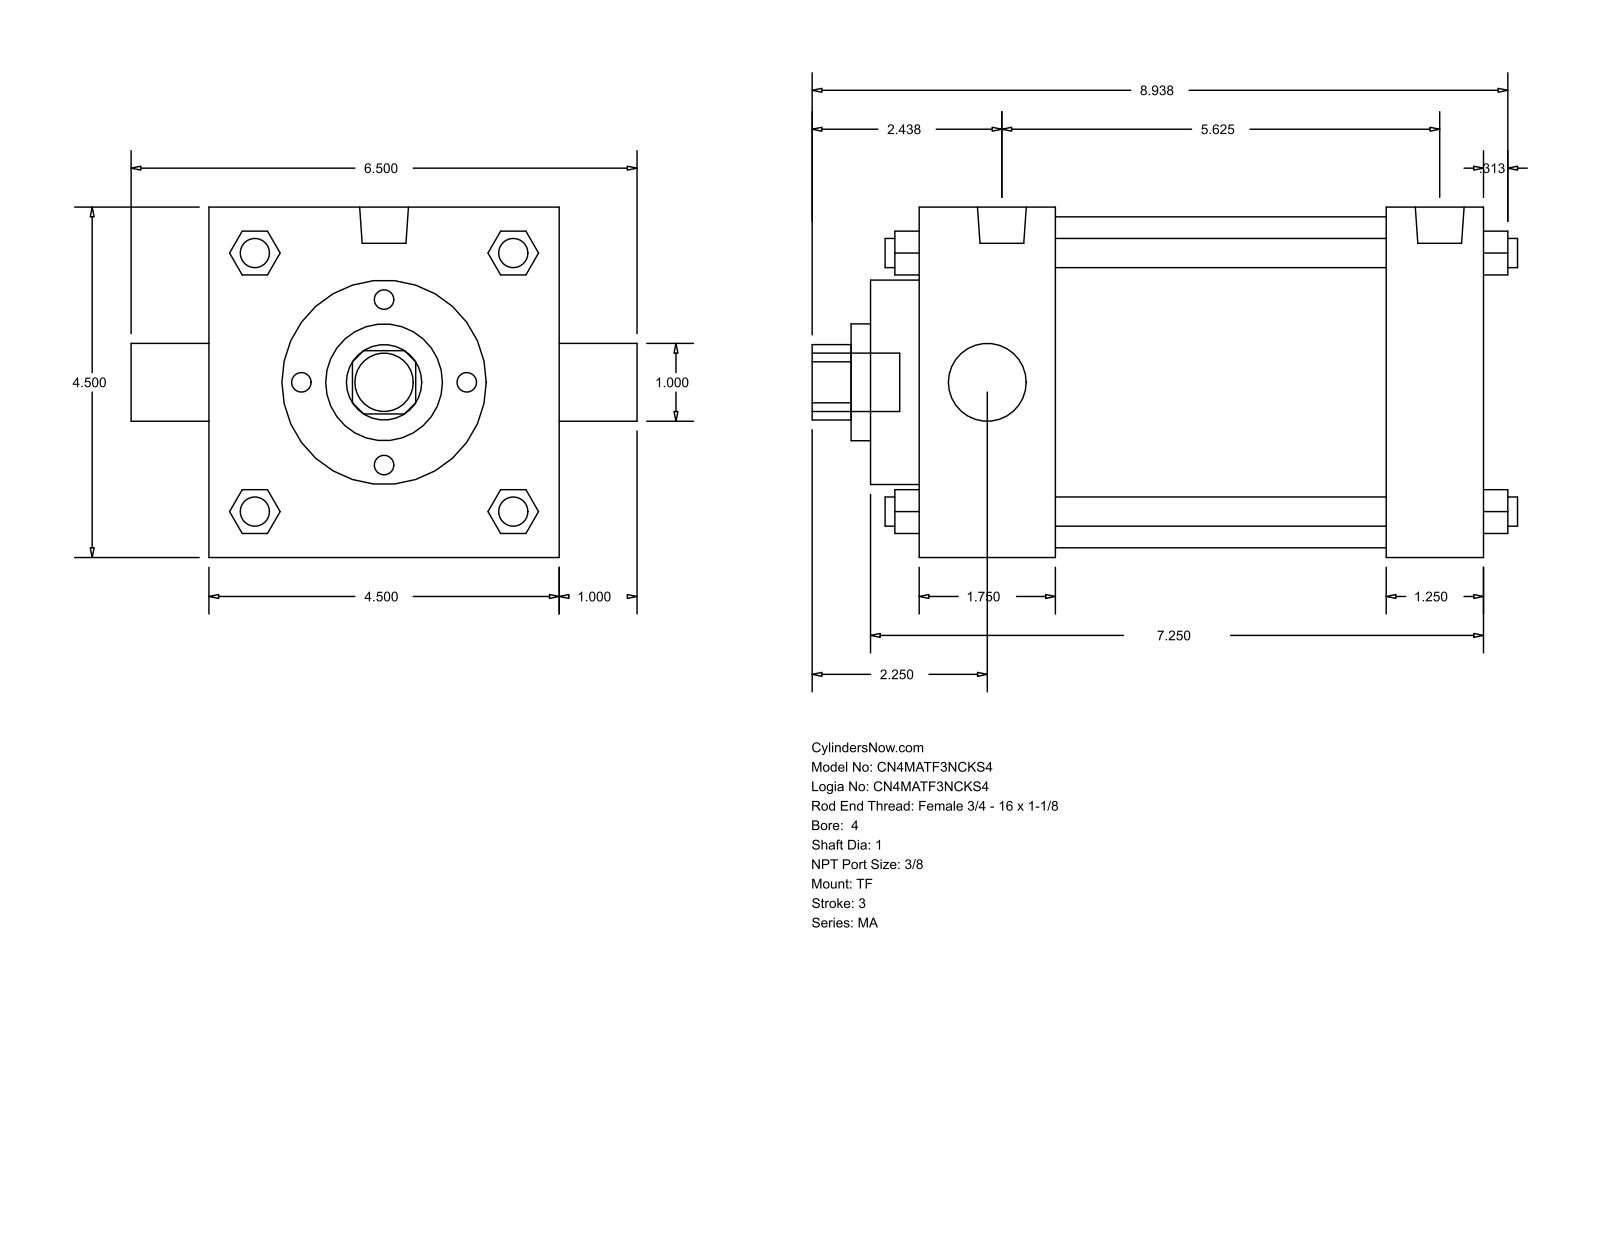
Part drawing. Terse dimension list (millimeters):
name: MA_TF__0400_1
written by: GSSL Pune (CONFIG_CONTROL_DESIGN)
unit: mm
bodies: 0 solids, 122 faces (93 planar, 29 cylindrical, 0 other)
size: 230.19 × 165.1 × 114.3
holes: 2× ⌀25.4, 1× ⌀38.1, 1× ⌀66.67, 1× ⌀107.95
bosses: 4× ⌀9.53, 3× ⌀11.11, 2× ⌀15.93, 1× ⌀19.05
rounds: 1× R12.29
face distances: 114.3, 184.15, 152.4, 31.75, 44.46, 107.94, 139.69, 200.02, 15.87, 60.33
